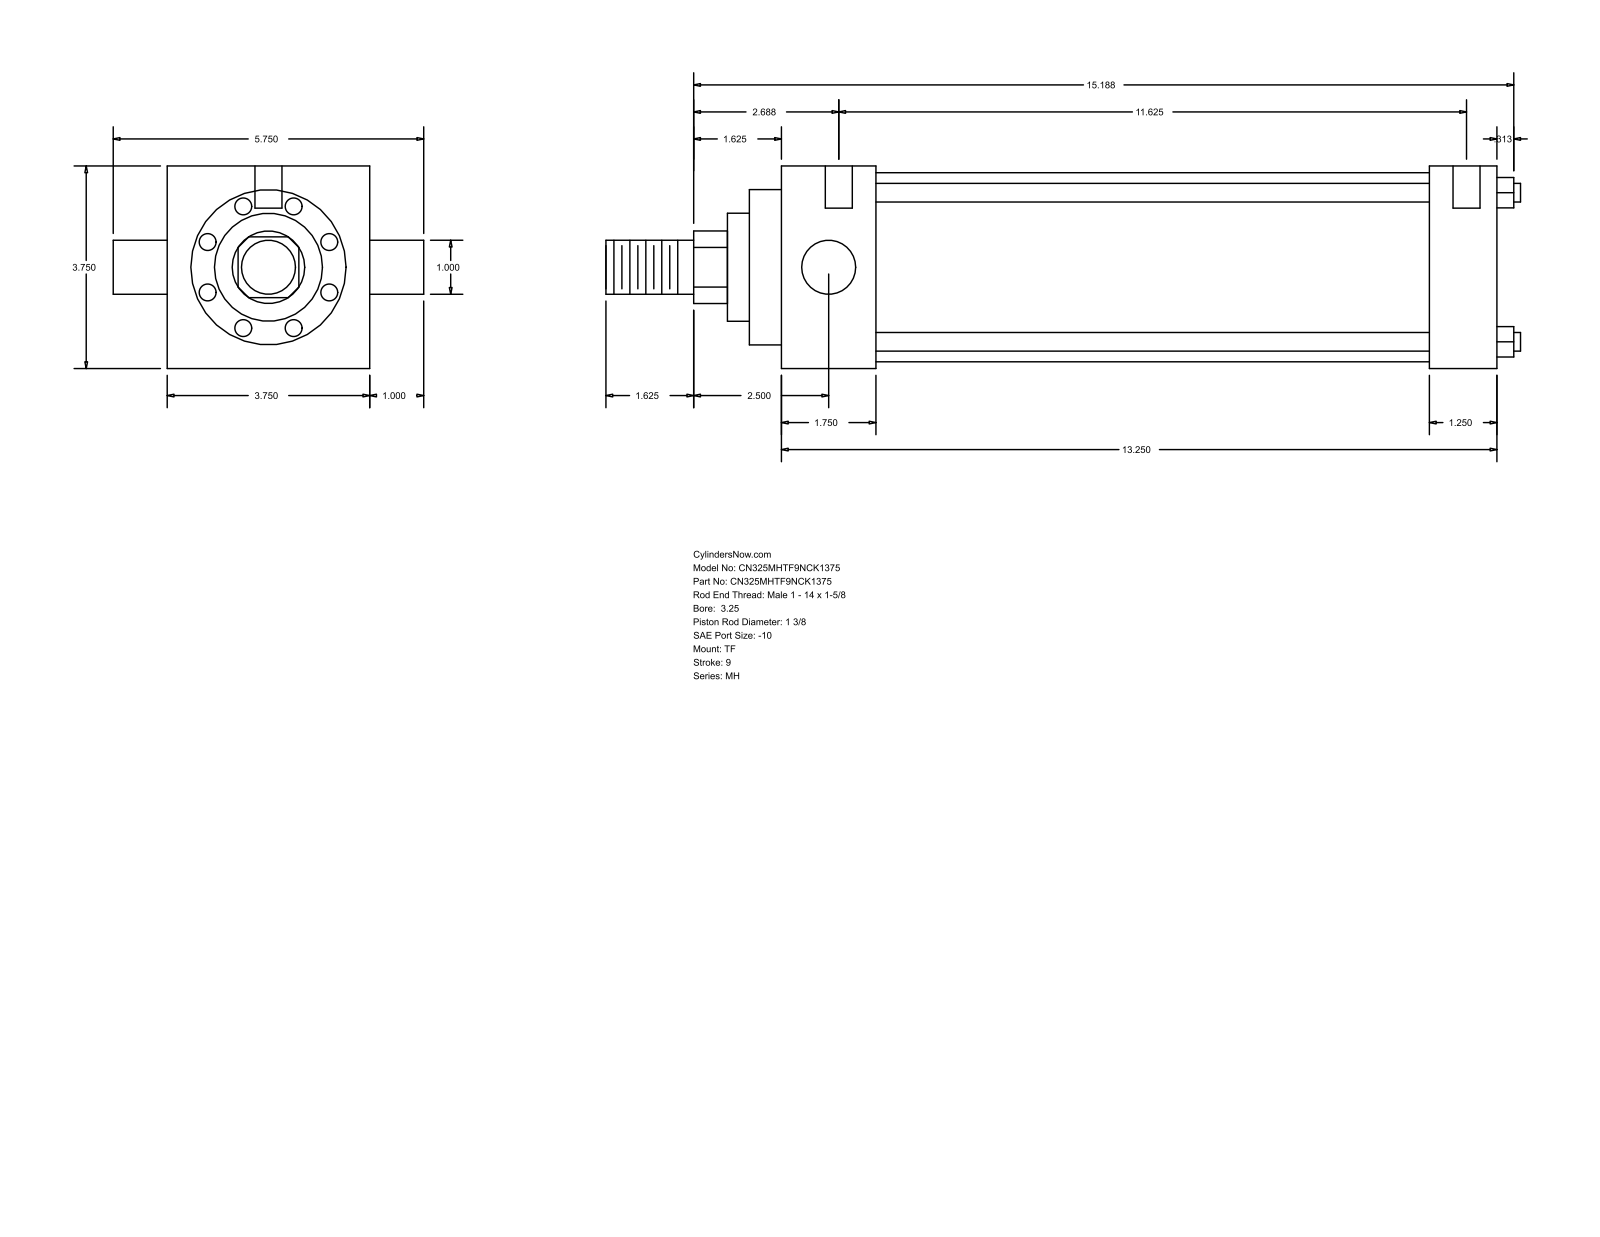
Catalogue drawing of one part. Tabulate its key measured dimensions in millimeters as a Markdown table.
| quantity | value |
| --- | --- |
| part name | MH_TF__0325_1.375 |
| STEP written by | GSSL Pune (CONFIG_CONTROL_DESIGN) |
| units | millimeters |
| bodies | 0 solids, 86 faces (61 planar, 25 cylindrical, 0 other) |
| overall size | 430.21 × 146.05 × 95.25 |
| round holes (diameter × count) | 5.56 × 3, 12.7 × 2 |
| round bosses / shafts (diameter × count) | 8.76 × 4, 25.4 × 2, 88.9 × 1, 73.03 × 1, 50.8 × 1, 34.92 × 1 |
| partial cylindrical surfaces (radius × count) | 17.06 × 1 |
| main face-to-face distances | 95.24, 336.55, 44.45, 304.8, 260.35, 292.1, 31.75, 15.08, 59.53, 319.88 |
| hole center spacings | 1.59, 4.76, 295.28, 296.87, 300.04, 301.63 |
